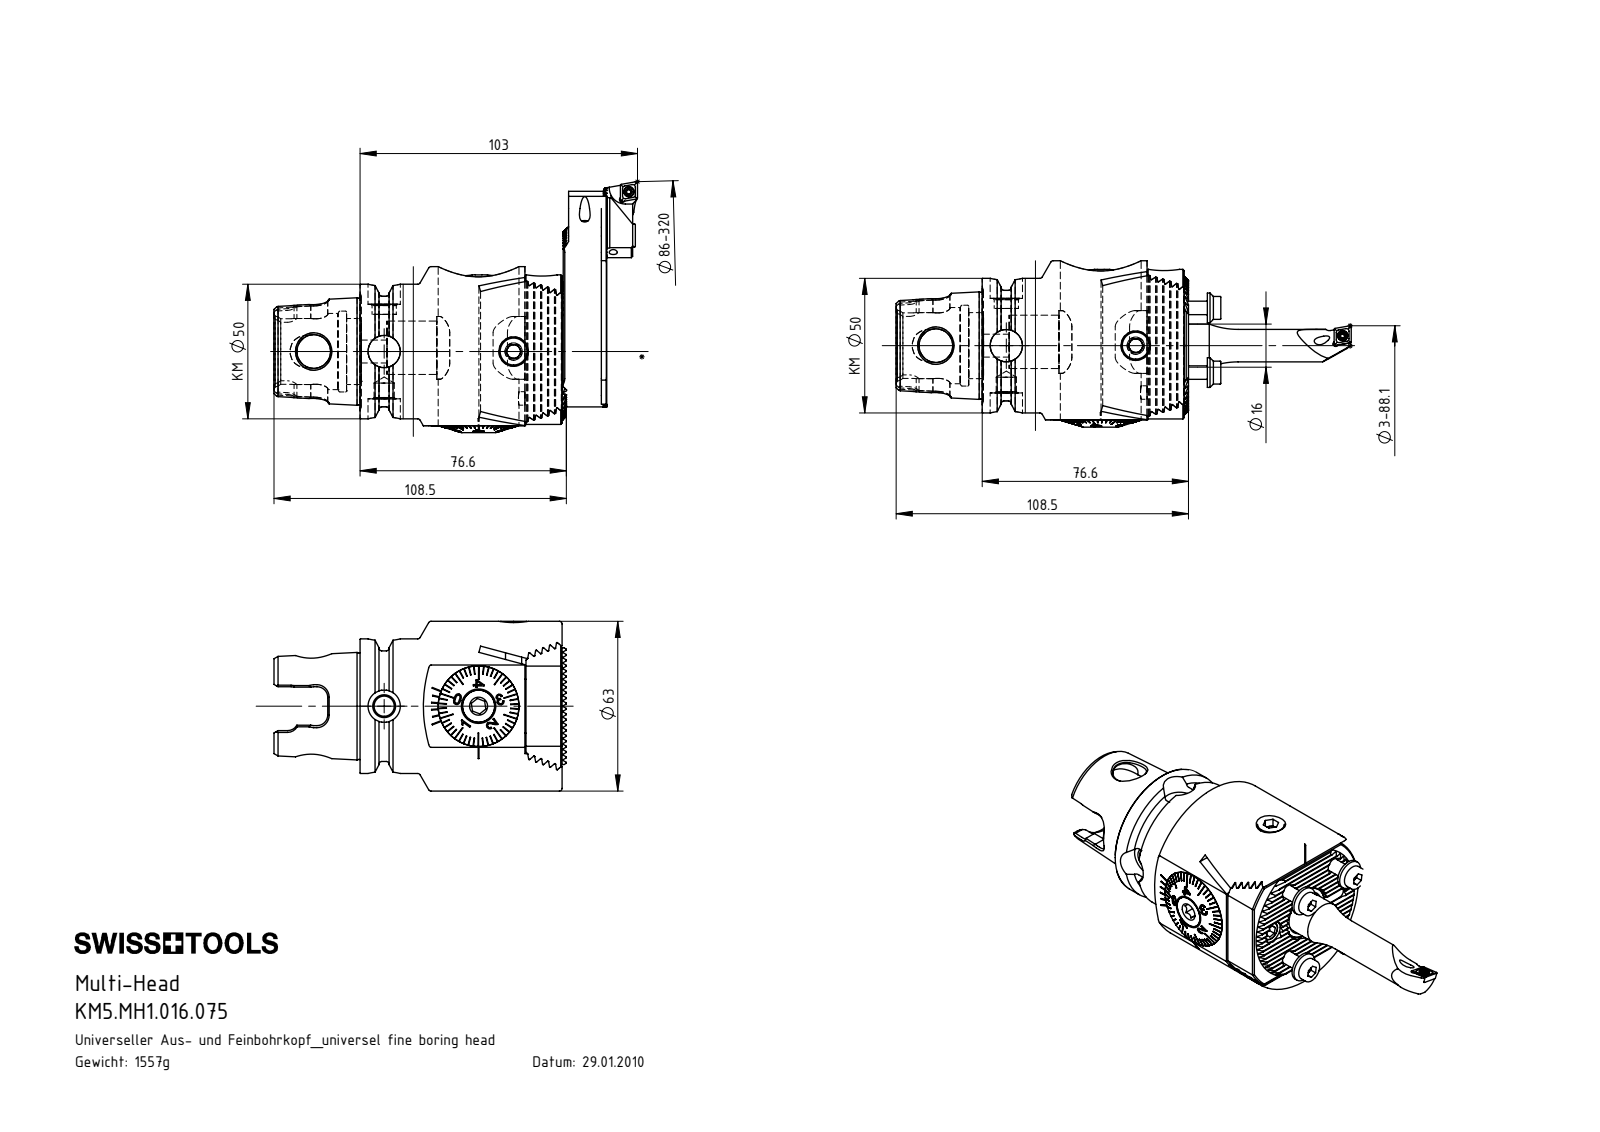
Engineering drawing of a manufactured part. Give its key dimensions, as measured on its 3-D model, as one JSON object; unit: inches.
{"part_name": "MH1-BG3.001.042_D; A55-BG1.012.007_B; A55-BG2.014.007_A; KU5.MH1.K01.075 (+8 more)", "step_written_by": "SolidWorks 2017 (AUTOMOTIVE_DESIGN)", "units": "inches", "bodies": {"solids": 15, "faces": 989, "planar": 558, "cylindrical": 192, "other": 239}, "overall_size": [4.273, 2.48, 2.431], "volume_in3": 11.34, "surface_area_in2": 102.2, "round_holes": [[0.165, 5], [0.335, 5], [0.268, 3], [0.433, 3], [0.197, 2], [0.472, 2], [0.787, 2], [0.039, 1], [0.063, 1], [0.13, 1], [0.252, 1], [0.295, 1]], "round_bosses_or_shafts": [[0.394, 3], [2.48, 1], [1.967, 1], [1.181, 1], [1.18, 1], [1.177, 1], [0.984, 1], [0.709, 1]], "partial_cylinders_radius": [[0.006, 21], [0.008, 20], [0.157, 8], [0.236, 6], [0.238, 2], [0.335, 2], [1.22, 2], [0.079, 1]], "face_to_face_distances": [0.094, 0.187, 0.016, 0.068, 0.341, 0.205, 0.094, 0.543, 0.528, 0.273], "hole_center_spacings": [0.659, 0.71, 0.808, 0.945, 1.181, 1.37, 1.513, 0.287]}
